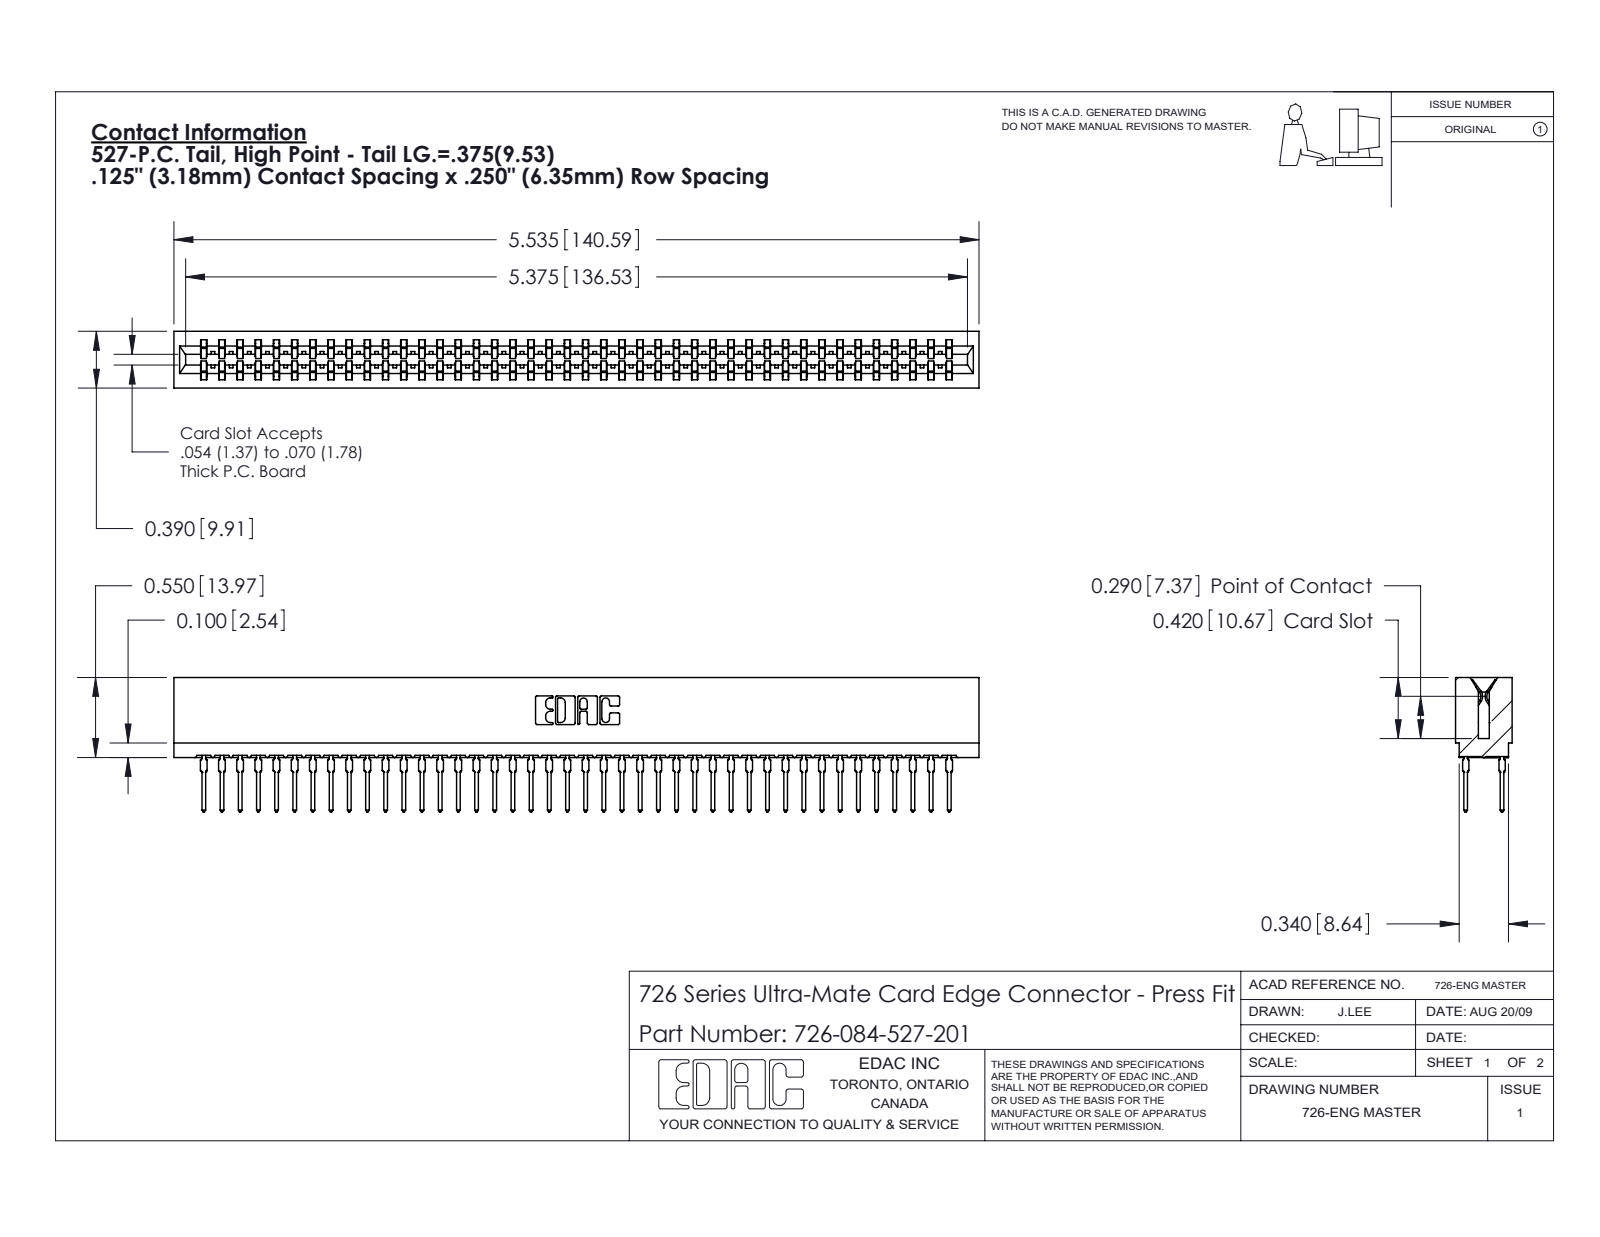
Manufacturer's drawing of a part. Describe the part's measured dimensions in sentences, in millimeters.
The part is named "746-292-001_527; 726-084-527-201; 726 Part_.515 Slot Depth - 01". Its 3-D file was written by "SolidWorks 2020 (CONFIG_CONTROL_DESIGN)". It is 85 solids with 7615 faces: 3919 planar, 1512 cylindrical and 2184 other. Overall it measures 140.6 by 23.5 by 9.9 millimeters. Its volume is 13 100 cubic millimeters and its surface area 22 460 square millimeters. Partial cylindrical surfaces (rounded edges, fillets, slot ends): 168 of radius 0.5, 43 of radius 0.4, 22 of radius 0.3, 8 of radius 0.1, 8 of radius 0.3, 6 of radius 0.2, 6 of radius 0.8, 3 of radius 0.7. The main face-to-face distances are 1.4, 8.5, 0.6, 7.8, 9.9, 6.4, 2.1, 7, 12.7, 9.3.
